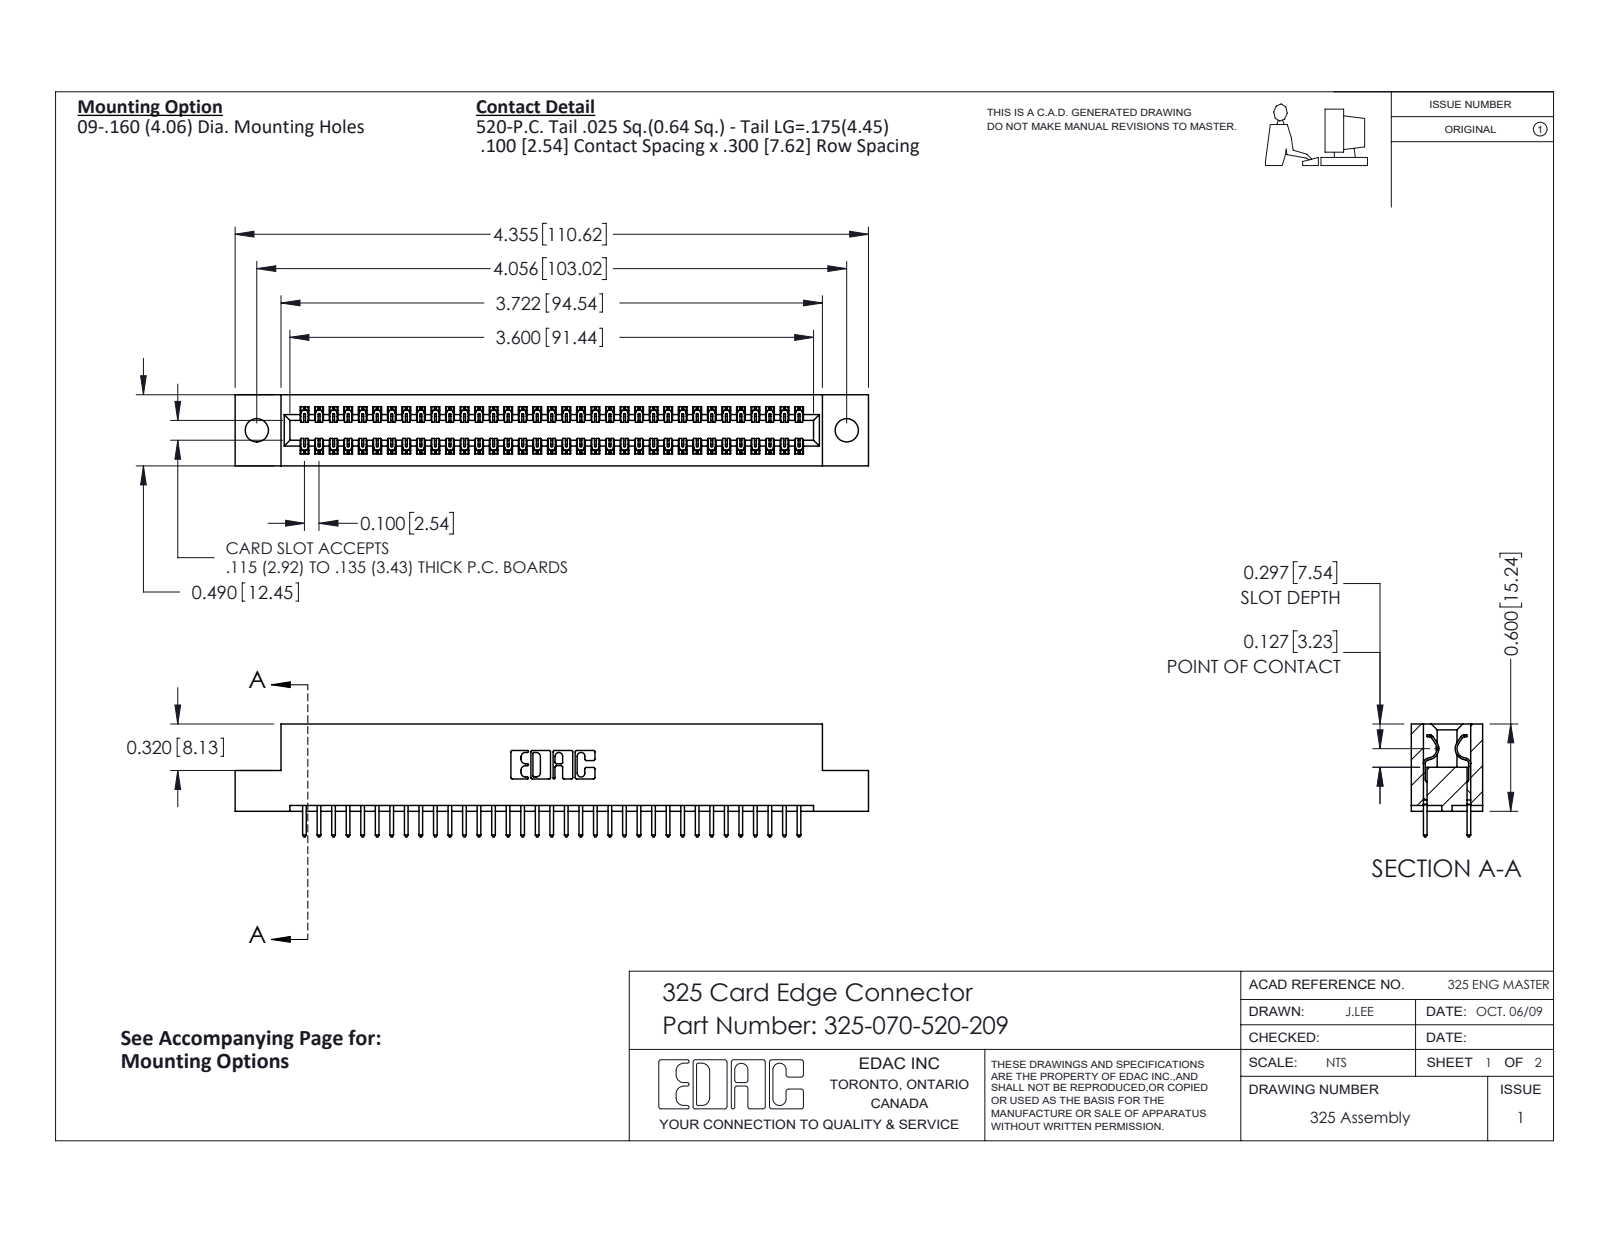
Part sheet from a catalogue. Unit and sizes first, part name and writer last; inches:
Units: inches
Overall size (bounding box): 4.355 × 0.775 × 0.49
Round holes (diameter × count): ⌀0.16 ×2
Partial cylindrical surfaces — rounded edges, fillets, slot ends (radius × count): R0.006 ×105, R0.01 ×70, R0.01 ×22, R0.007 ×6, R0.031 ×6, R0.026 ×3, R0.014 ×2, R0.022 ×2
Main face-to-face distances: 0.083, 0.407, 0.49, 0.3, 0.107, 0.383, 0.025, 0.325, 0.275, 0.56
Hole centre spacings: 4.056
Volume: 0.853 in³ · Surface area: 25.62 in²
Bodies: 71 solids, 3754 faces (2590 planar, 1164 cylindrical, 0 other)
Part name (STEP PRODUCT): 325-070-520-209; 325-292-001_325-293-120; 325 Part_.160 TH
STEP written by: SolidWorks 2016 (CONFIG_CONTROL_DESIGN)
